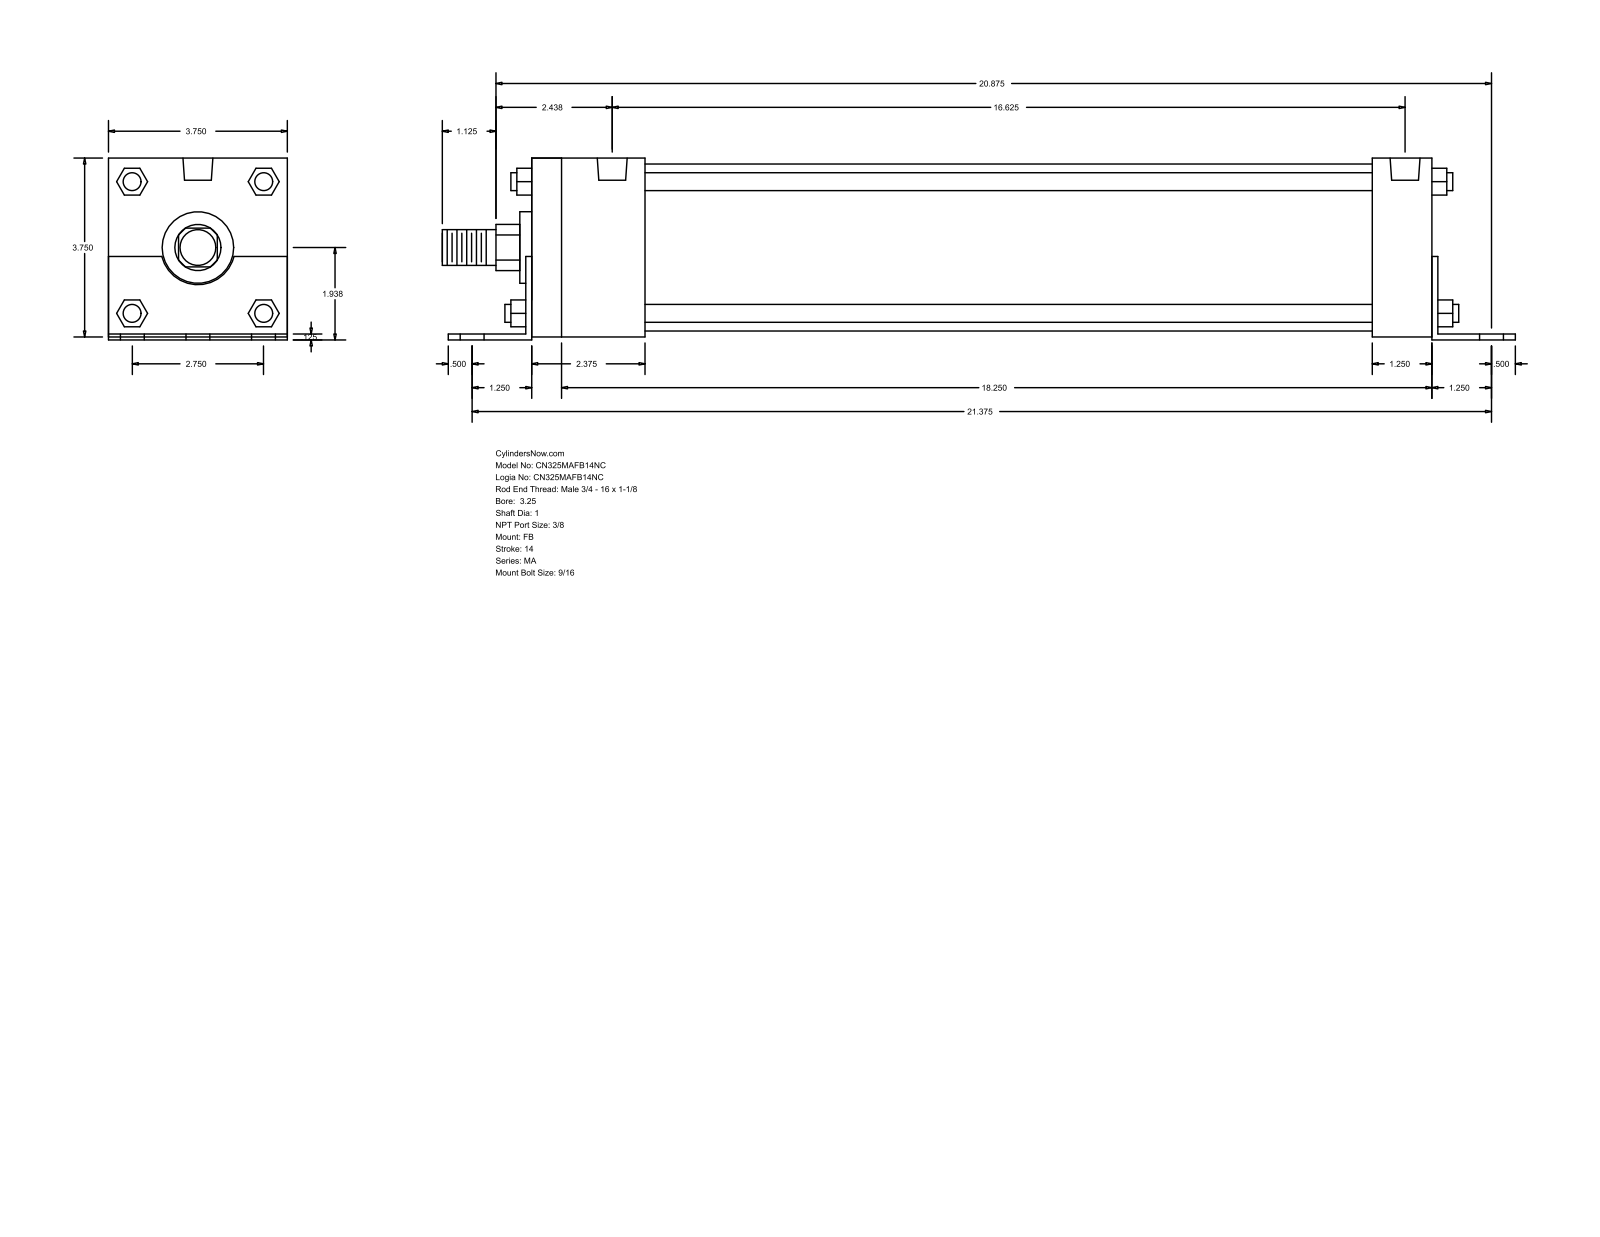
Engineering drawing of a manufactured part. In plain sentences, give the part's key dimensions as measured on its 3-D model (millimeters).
The part is named "MA_FB__0325_1". Its 3-D file was written by "GSSL Pune (CONFIG_CONTROL_DESIGN)". It is 0 solids with 140 faces: 105 planar, 35 cylindrical and 0 other. Overall it measures 571.5 by 96.84 by 95.25 millimeters. Round holes: 6 of diameter 14.29, 4 of diameter 11.11, 2 of diameter 15.93. Round bosses or shafts: 4 of diameter 9.53, 1 of diameter 88.9, 1 of diameter 38.1, 1 of diameter 25.4, 1 of diameter 19.05. Partial cylindrical surfaces (rounded edges, fillets, slot ends): 1 of radius 12.29, 1 of radius 19.81. The main face-to-face distances are 95.24, 3.17, 1.59, 96.83, 1.58, 93.66, 482.6, 479.43, 485.77, 450.85. The hole center spacings are 34.92, 544.05, 542.93, 4.76, 57.78, 61.64, 69.84, 82.38.
